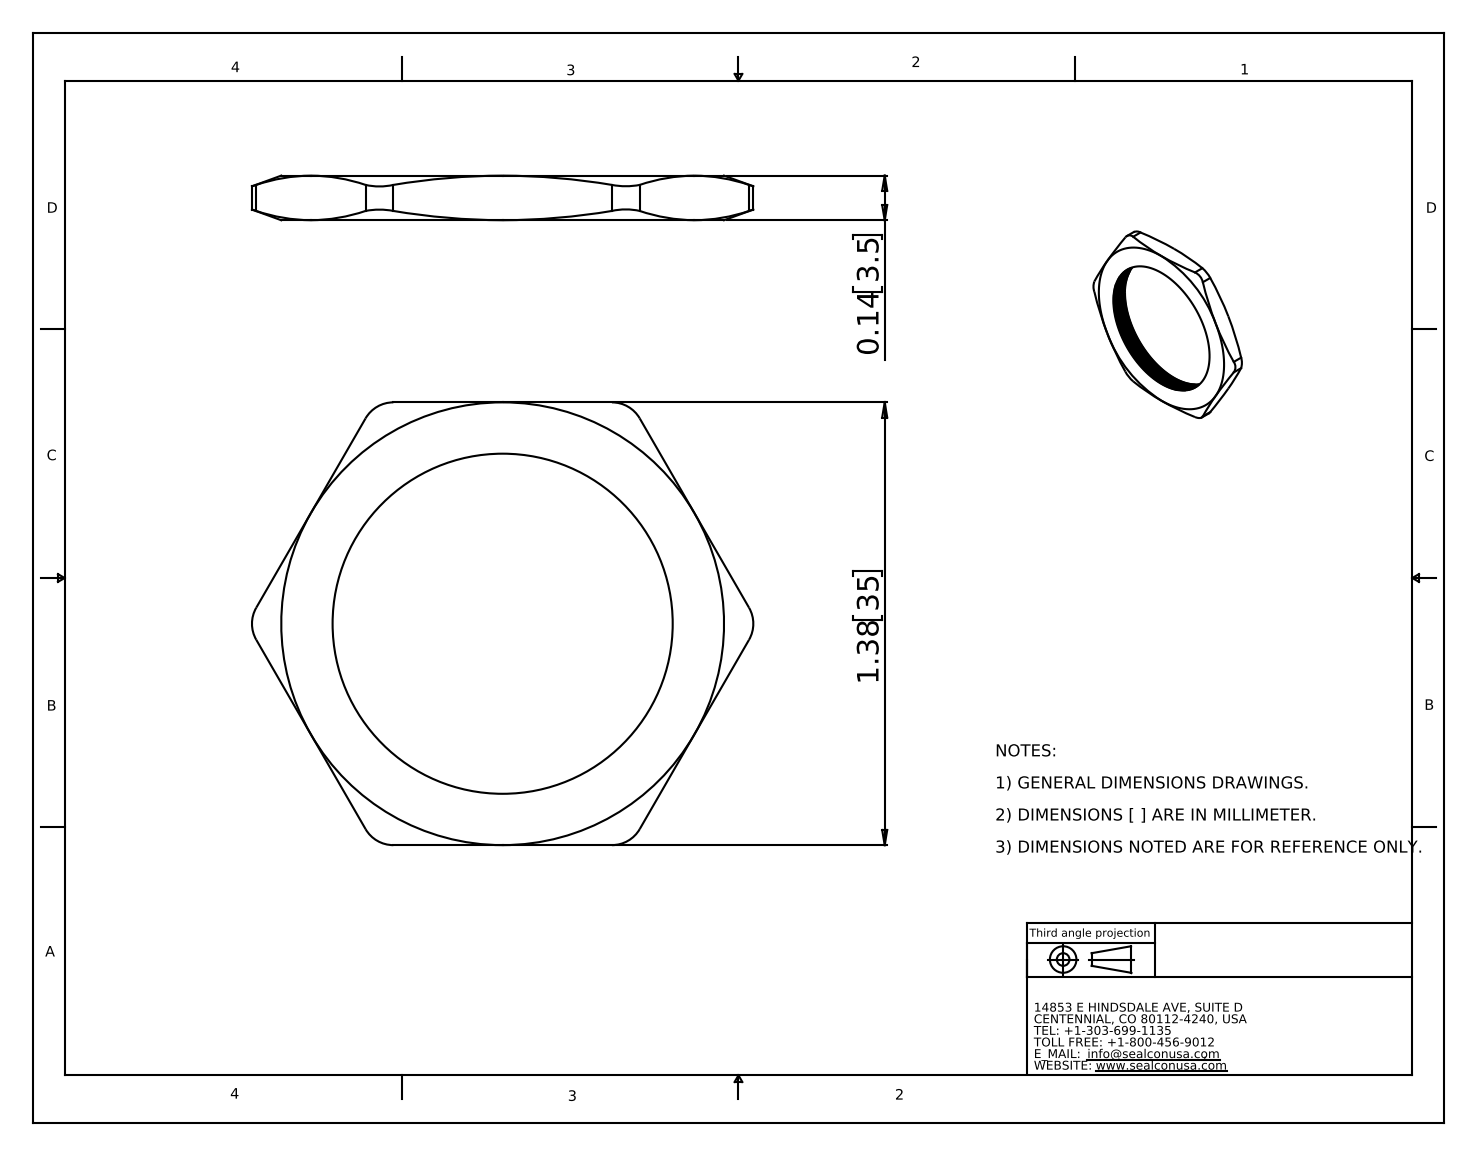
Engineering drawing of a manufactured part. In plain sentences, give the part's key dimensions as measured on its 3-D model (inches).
The part is named "NN-29-BR". Its 3-D file was written by "SolidWorks 2007 (CONFIG_CONTROL_DESIGN)". It is 1 solid with 97 faces: 8 planar, 7 cylindrical and 82 other. Overall it measures 1.563 by 1.38 by 0.14 inches. Its volume is 0.098 cubic inches and its surface area 3.007 square inches. Partial cylindrical surfaces (rounded edges, fillets, slot ends): 6 of radius 0.1. The main face-to-face distances are 0.14, 1.38.
